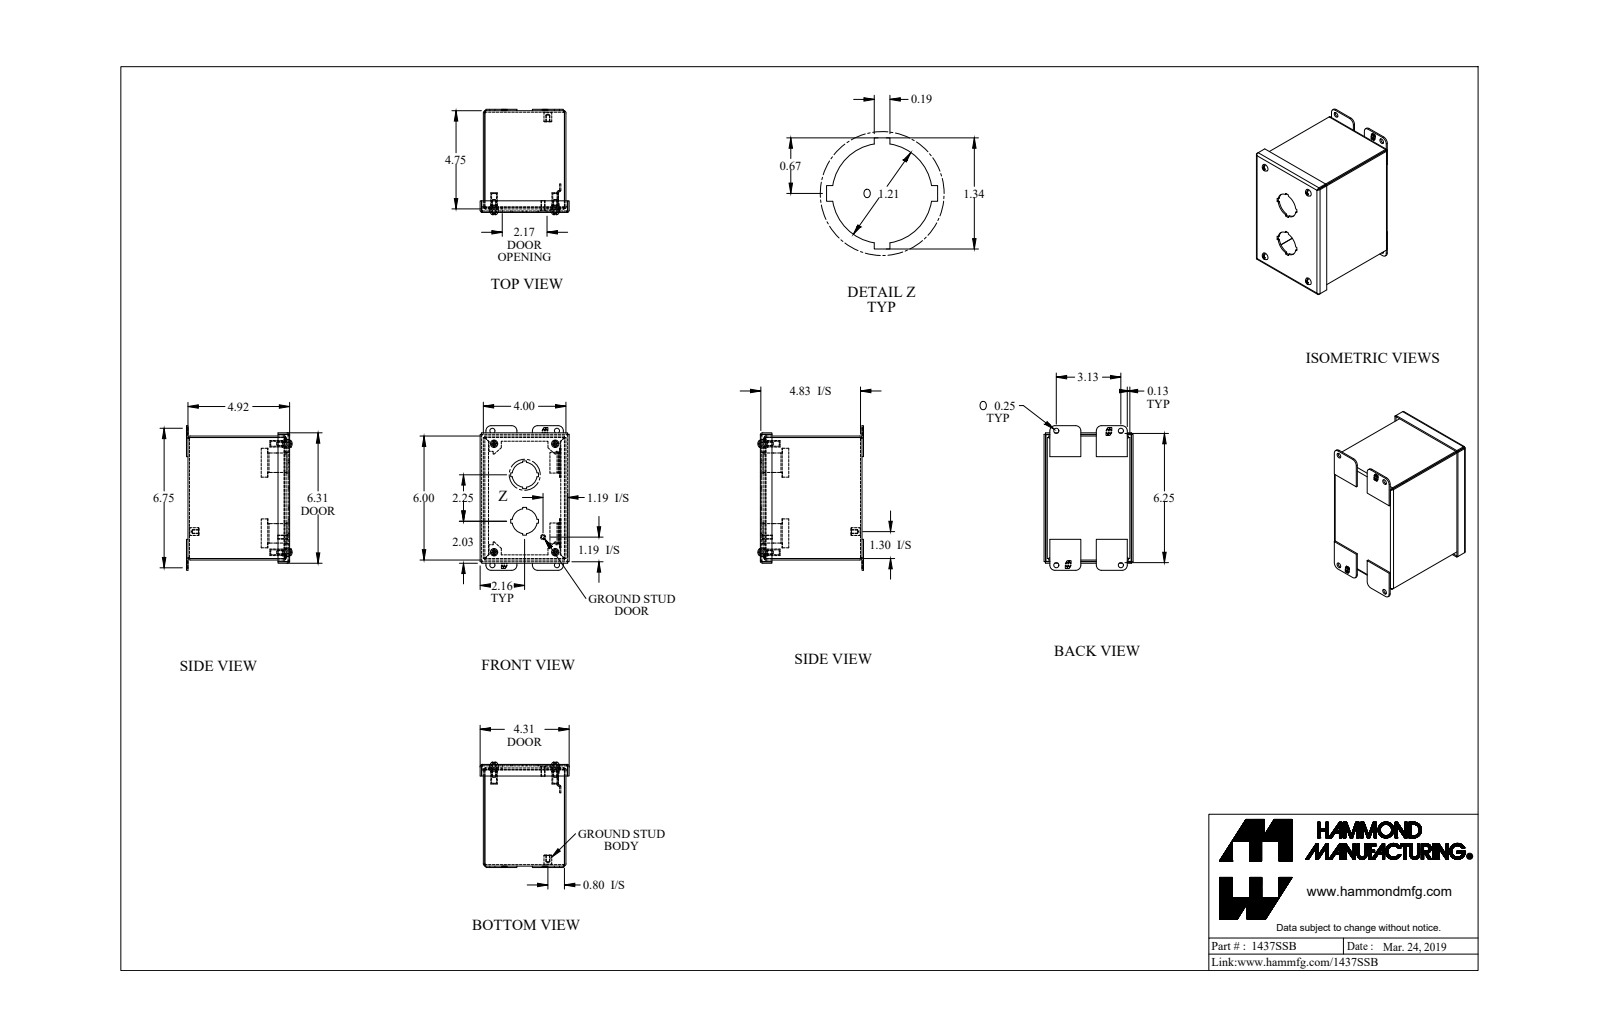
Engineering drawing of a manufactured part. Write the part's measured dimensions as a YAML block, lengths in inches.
part_name: "1437SSB_Default"
step_written_by: "SolidWorks 2019 (CONFIG_CONTROL_DESIGN)"
units: inches
bodies: {solids: 23, faces: 637, planar: 447, cylindrical: 160, other: 30}
overall_size: [7, 5.104, 4.312]
volume: 13.98
surface_area: 376.1
round_holes:
  - {diameter: 0.25, count: 8}
  - {diameter: 0.065, count: 4}
  - {diameter: 0.239, count: 4}
  - {diameter: 0.253, count: 4}
  - {diameter: 0.406, count: 4}
  - {diameter: 1.21, count: 2}
  - {diameter: 0.156, count: 1}
round_bosses_or_shafts:
  - {diameter: 0.19, count: 5}
  - {diameter: 0.406, count: 4}
  - {diameter: 0.315, count: 4}
  - {diameter: 0.148, count: 4}
  - {diameter: 0.375, count: 1}
  - {diameter: 0.25, count: 1}
partial_cylinders:
  - {radius: 0.036, count: 12}
  - {radius: 0.108, count: 12}
  - {radius: 0.25, count: 8}
  - {radius: 0.029, count: 4}
  - {radius: 0.086, count: 4}
  - {radius: 0.171, count: 4}
  - {radius: 0.125, count: 3}
face_to_face_distances: [0.072, 3.928, 4.85, 5.928, 4.922, 3.856, 4, 4.778, 0.156, 5.856]
hole_center_spacings: [5.25, 5.875, 2.961, 3.107, 0.63, 0.631, 2.107, 2.108]
